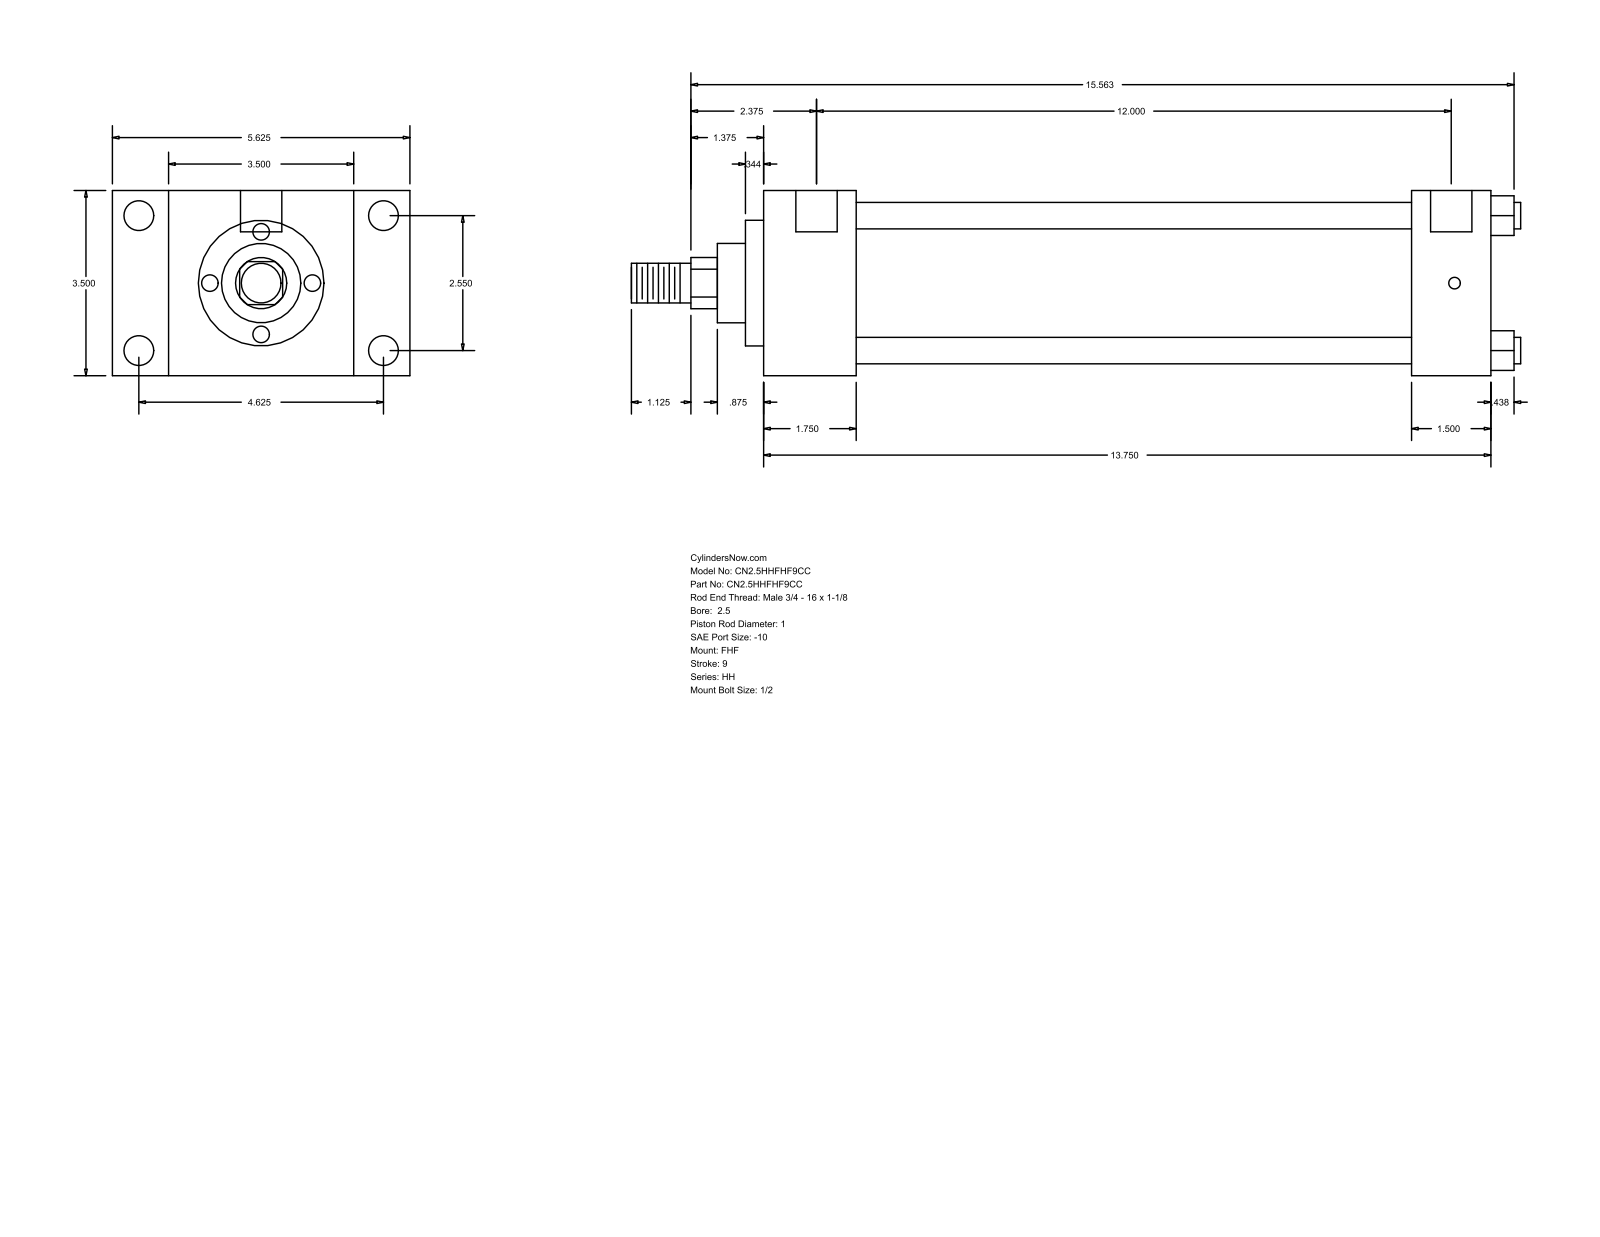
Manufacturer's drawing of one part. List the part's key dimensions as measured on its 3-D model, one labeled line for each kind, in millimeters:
Part name (STEP PRODUCT): HH_FHF__0250_1
STEP written by: GSSL Pune (CONFIG_CONTROL_DESIGN)
Units: millimetres
Bodies: 0 solids, 90 faces (61 planar, 29 cylindrical, 0 other)
Overall size (bounding box): 427.04 × 142.88 × 88.9
Round holes (diameter × count): ⌀5.56 ×4, ⌀14.3 ×4, ⌀19.84 ×2
Round bosses / shafts (diameter × count): ⌀12.7 ×4, ⌀73.03 ×1, ⌀60.33 ×1, ⌀38.1 ×1, ⌀25.4 ×1, ⌀19.05 ×1
Partial cylindrical surfaces — rounded edges, fillets, slot ends (radius × count): R12.29 ×1
Main face-to-face distances: 88.9, 44.46, 26.99, 115.89, 349.26, 304.8, 142.88, 311.15, 266.69, 38.11
Hole centre spacings: 1.59, 64.76, 117.48, 134.15, 306.38, 307.97, 304.79
